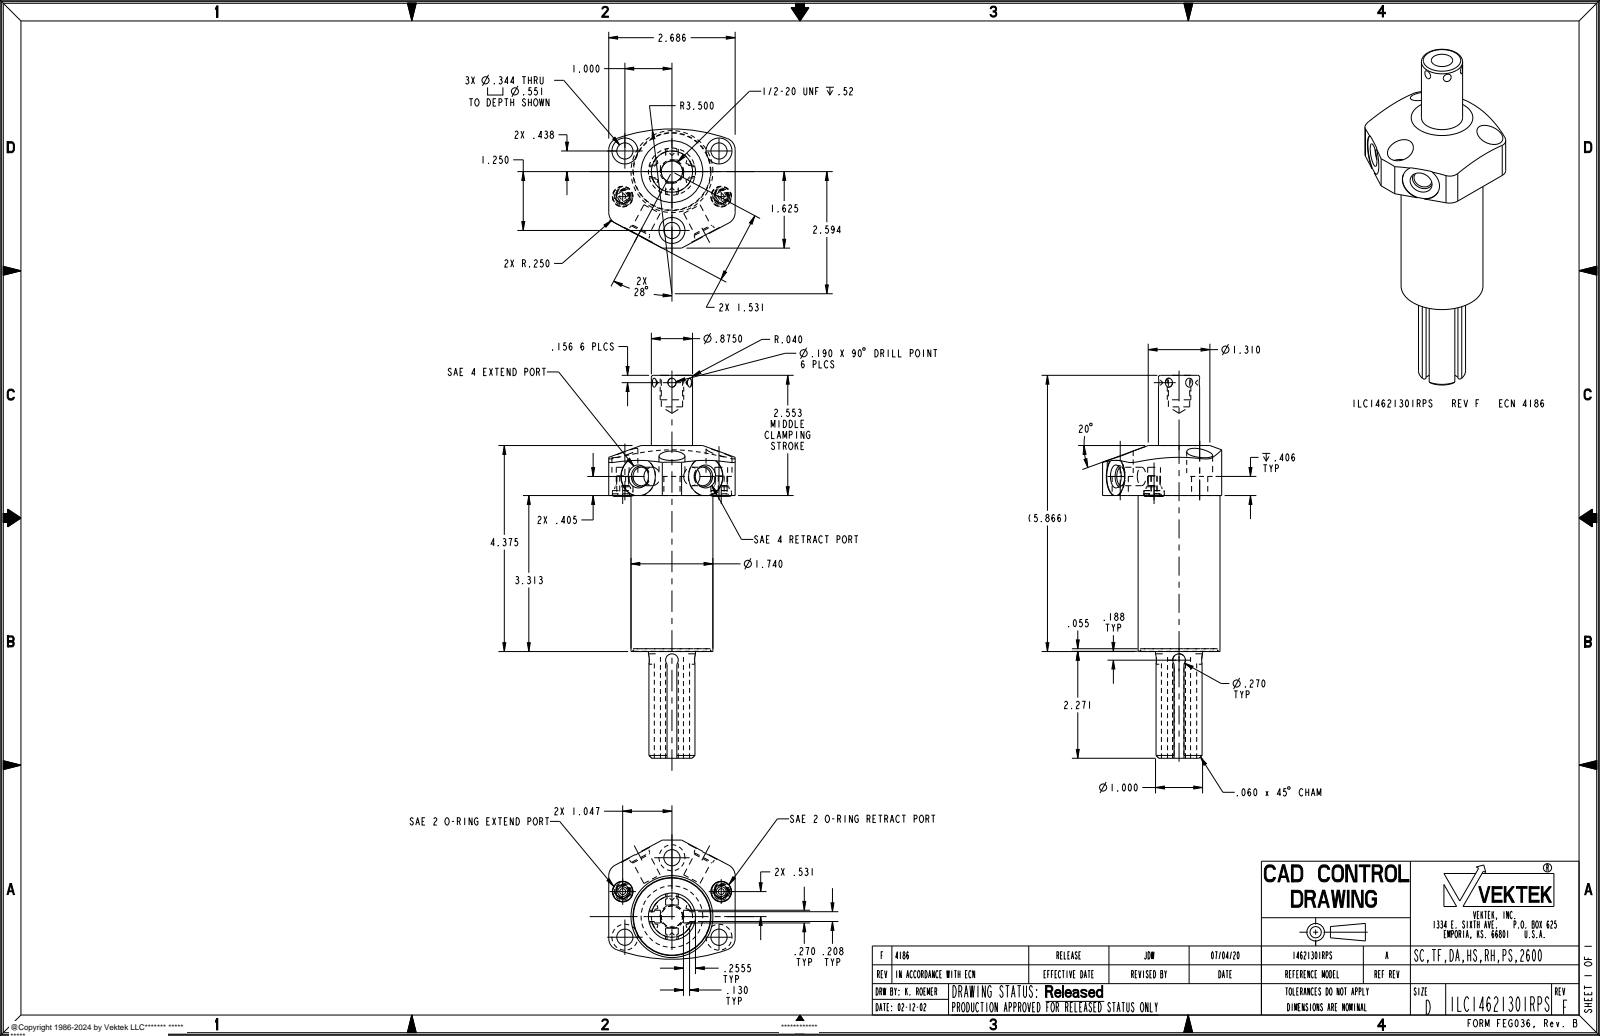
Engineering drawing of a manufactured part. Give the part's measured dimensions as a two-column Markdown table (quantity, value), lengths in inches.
| quantity | value |
| --- | --- |
| part name | ILC14621301RPS |
| STEP written by | PRO/ENGINEER BY PARAMETRIC TECHNOLOGY CORPORATION, 2013320 (AUTOMOTIVE_DESIGN) |
| units | inches |
| bodies | 1 solid, 177 faces (64 planar, 67 cylindrical, 46 other) |
| overall size | 8.132 × 2.686 × 2.531 |
| volume | 14.71 in³ |
| surface area | 63.43 in² |
| round holes (diameter × count) | 0.344 × 3, 0.551 × 3, 0.125 × 2, 0.272 × 2, 0.392 × 2, 0.438 × 2, 0.453 × 1, 1.656 × 1 |
| round bosses / shafts (diameter × count) | 0.43 × 2, 0.256 × 2, 0.21 × 2, 1.74 × 1, 1.636 × 1, 1 × 1, 0.875 × 1, 0.5 × 1 |
| partial cylindrical surfaces (radius × count) | 0.25 × 4, 0.135 × 2, 0.412 × 2, 3.5 × 1 |
| main face-to-face distances | 0.109, 0.38, 0.141, 0.348, 0.031, 0.239, 3.308, 1.098, 1.587, 0.489 |
| hole center spacings | 0.97, 1.092, 1.174, 1.27, 1.962, 2.265, 1.25, 2 |
